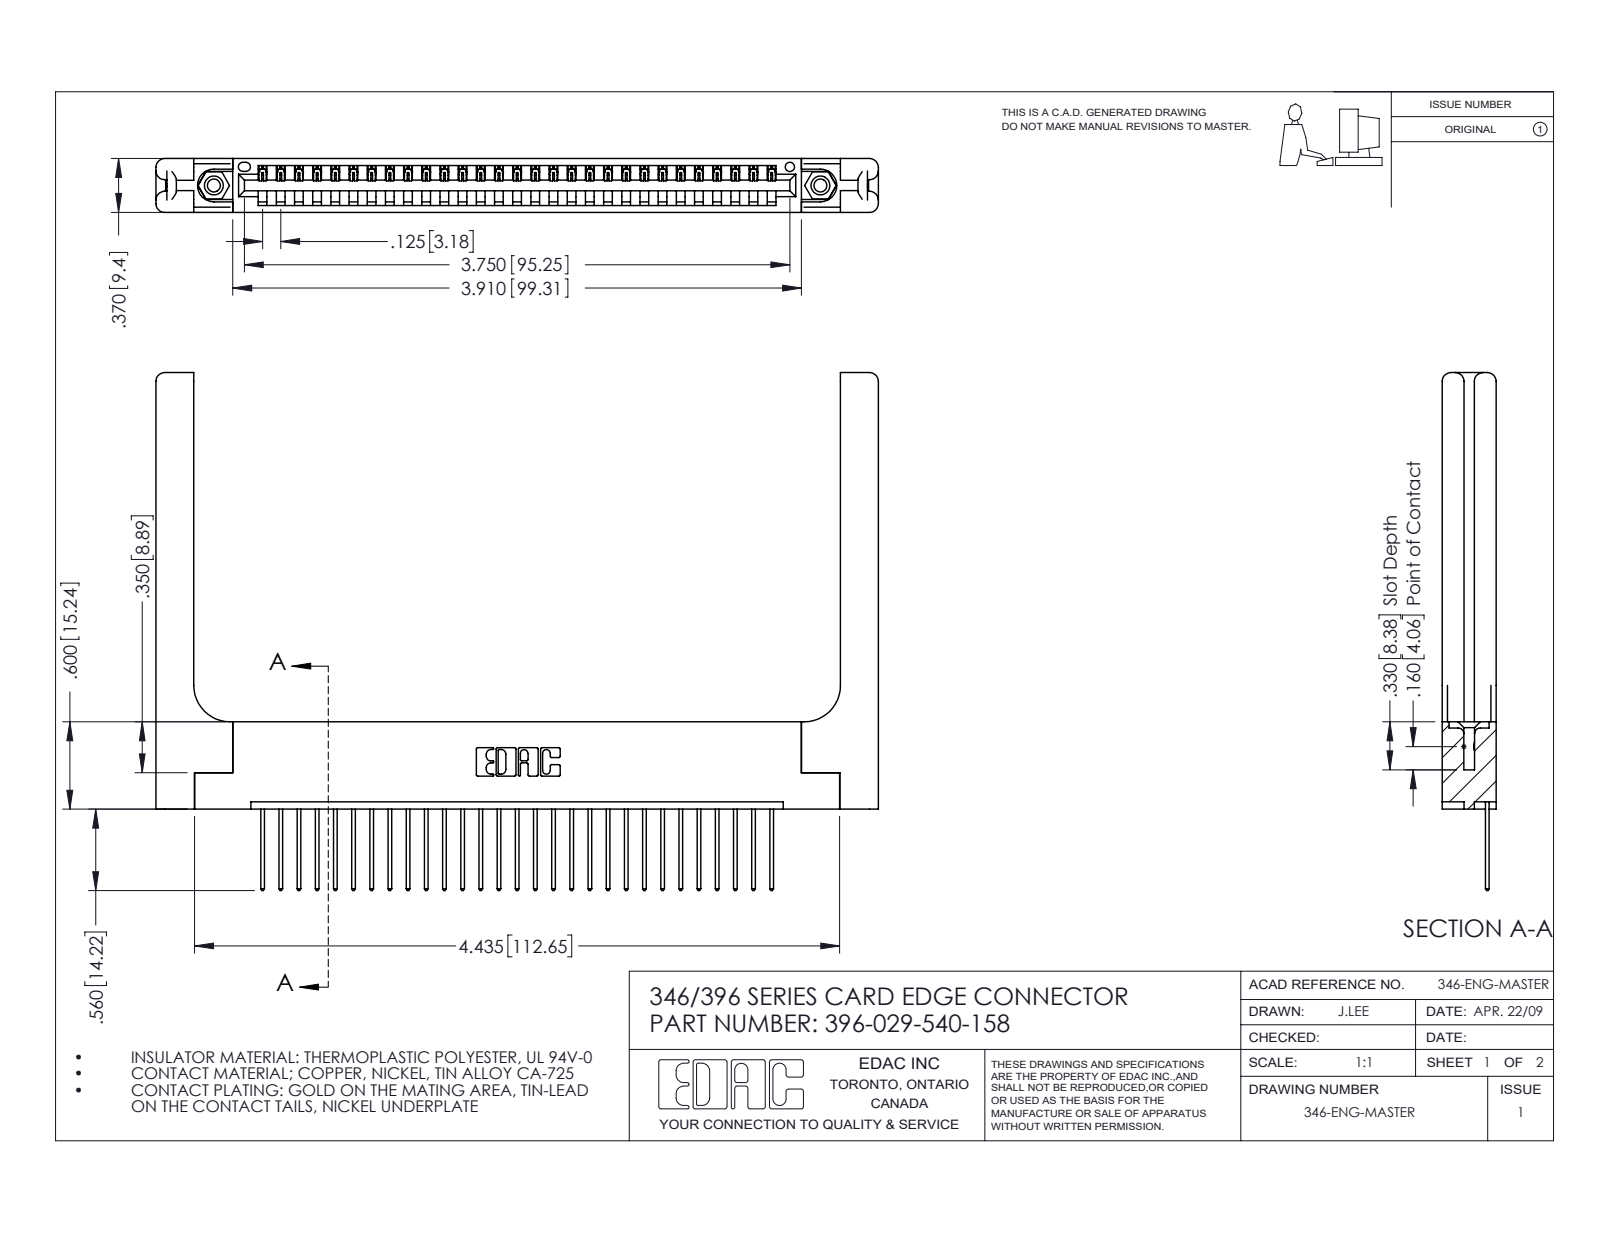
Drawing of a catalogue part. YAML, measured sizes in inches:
part_name: "346 Part_Flush Mounting Lugs - 0.156 Dia-TH; 396-029-540-158; 346-220-058_345-220-058; 345-250-001_345-250-001-102 (+1 more)"
step_written_by: "SolidWorks 2016 (CONFIG_CONTROL_DESIGN)"
units: inches
bodies: {solids: 34, faces: 2060, planar: 1384, cylindrical: 616, other: 60}
overall_size: [4.966, 3.56, 0.37]
volume: 1.193
surface_area: 31.53
round_holes:
  - {diameter: 0.089, count: 2}
  - {diameter: 0.125, count: 2}
  - {diameter: 0.156, count: 2}
  - {diameter: 0.064, count: 1}
round_bosses_or_shafts:
  - {diameter: 0.155, count: 2}
partial_cylinders:
  - {radius: 0.006, count: 58}
  - {radius: 0.01, count: 58}
  - {radius: 0.01, count: 22}
  - {radius: 0.06, count: 16}
  - {radius: 0.007, count: 6}
  - {radius: 0.031, count: 6}
  - {radius: 0.026, count: 3}
  - {radius: 0.03, count: 2}
face_to_face_distances: [0.37, 0.072, 0.048, 0.322, 0.148, 0.15, 0.25, 0.298, 0.025, 0.076]
hole_center_spacings: [0.246, 3.962, 4.17]
